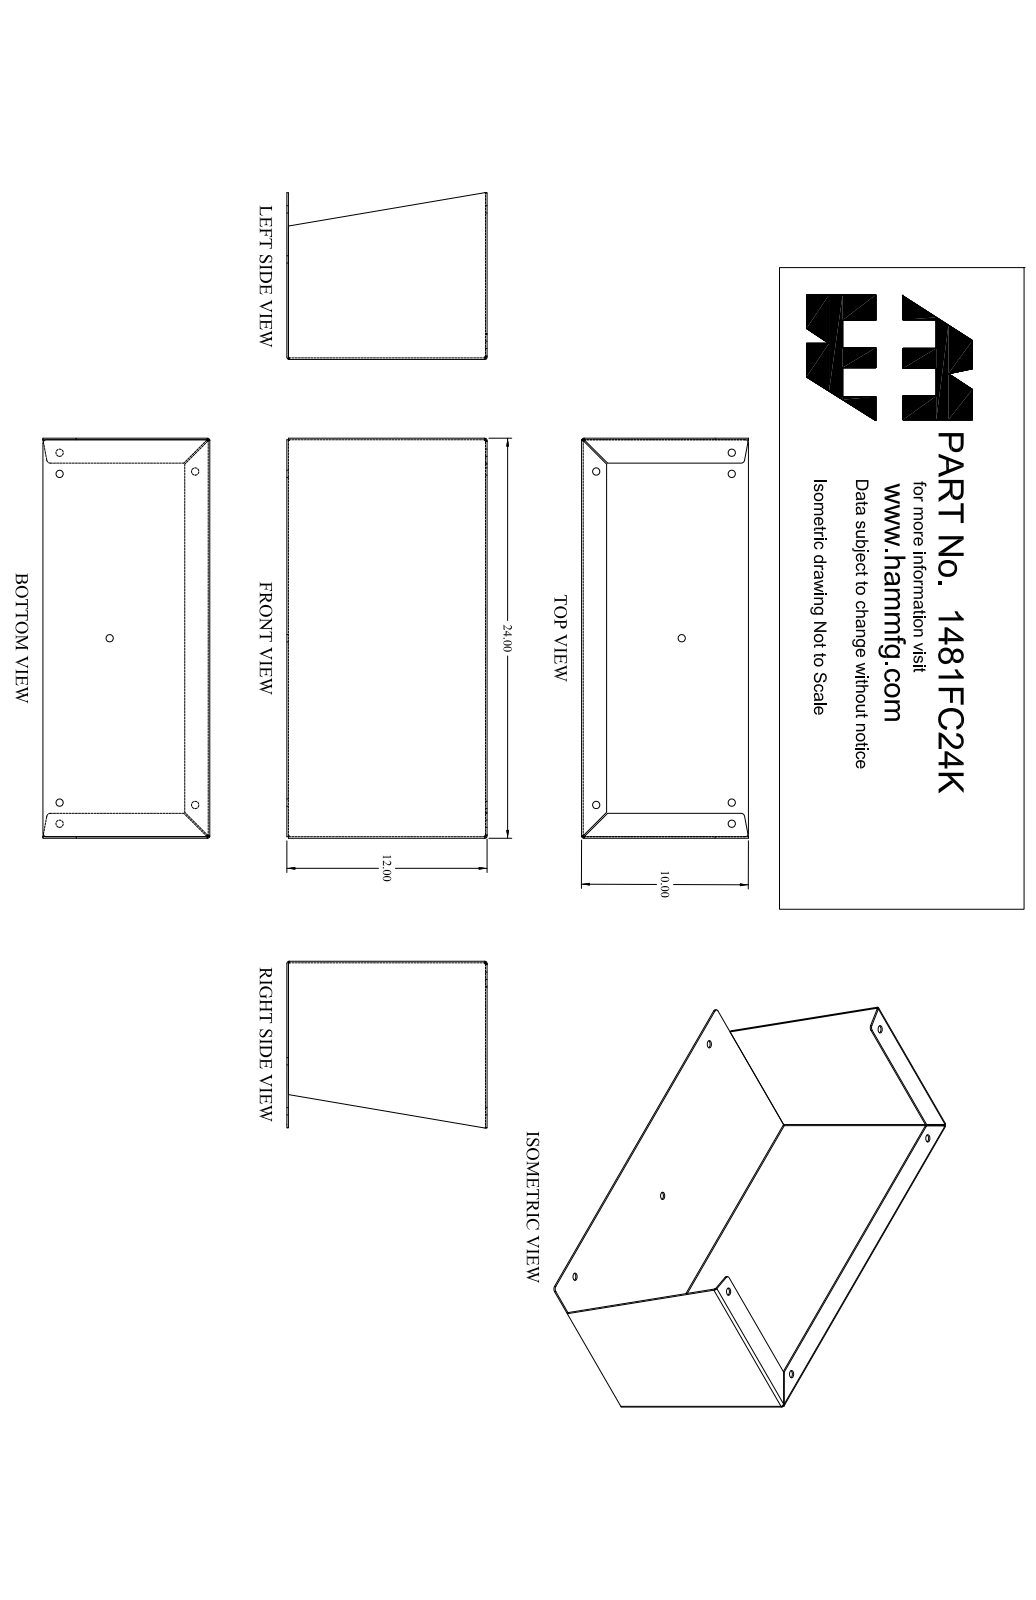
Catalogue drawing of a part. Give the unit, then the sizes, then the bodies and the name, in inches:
Units: inches
Overall size (bounding box): 24 × 12 × 10
Round holes (diameter × count): ⌀0.437 ×7
Partial cylindrical surfaces — rounded edges, fillets, slot ends (radius × count): R0.048 ×6, R0.143 ×6, R0.22 ×4
Main face-to-face distances: 0.095, 0.095, 23.905, 24, 23.81, 11.81, 11.905, 11.905, 12, 1.405
Hole centre spacings: 8.126, 8.202, 10.306, 11.237, 21.457, 1.266, 1.266, 11.522
Volume: 74.85 in³ · Surface area: 1 589 in²
Bodies: 1 solid, 78 faces (42 planar, 30 cylindrical, 6 other)
Part name (STEP PRODUCT): 1481FC24K_Default
STEP written by: SolidWorks 2019 (CONFIG_CONTROL_DESIGN)
